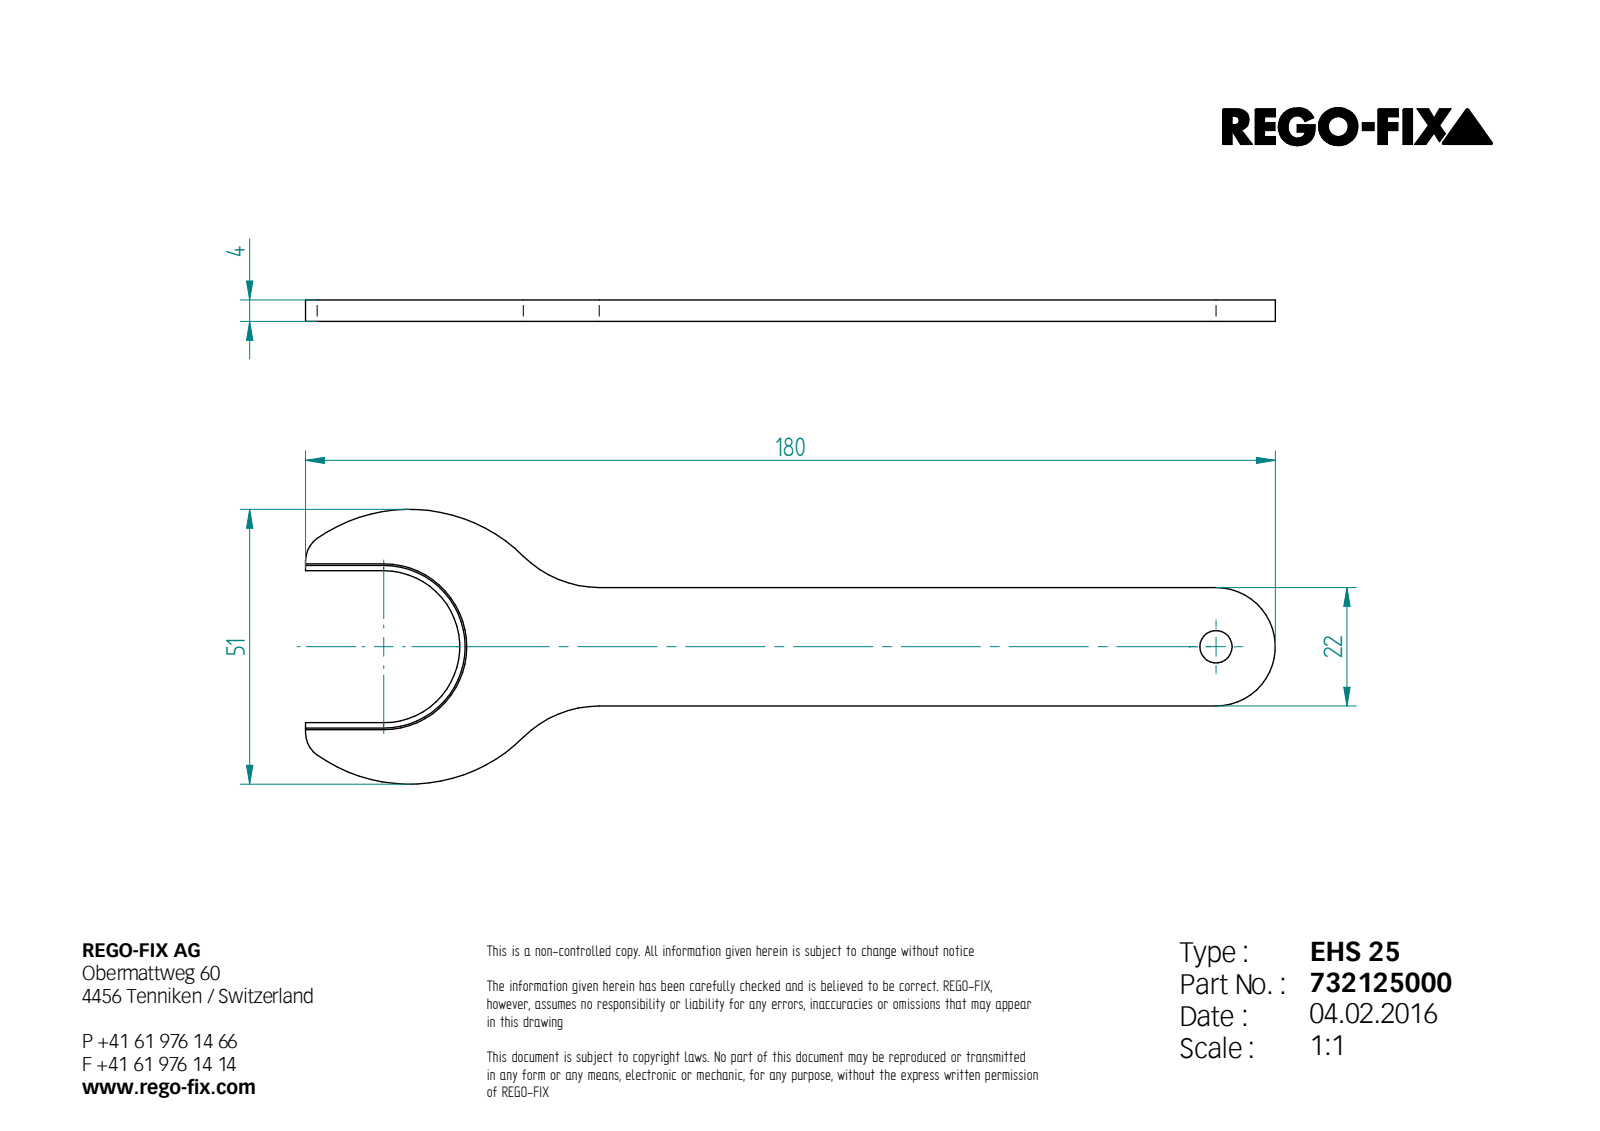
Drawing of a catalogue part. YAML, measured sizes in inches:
step_written_by: "Unknown (AUTOMOTIVE_DESIGN)"
units: inches
bodies: {solids: 1, faces: 23, planar: 12, cylindrical: 9, other: 2}
overall_size: [7.087, 2.008, 0.157]
volume: 1.004
surface_area: 15.87
round_holes:
  - {diameter: 0.236, count: 1}
partial_cylinders:
  - {radius: 0.197, count: 2}
  - {radius: 0.787, count: 2}
  - {radius: 1.181, count: 2}
  - {radius: 0.433, count: 1}
  - {radius: 0.594, count: 1}
face_to_face_distances: [0.157, 0.866, 0.161, 1.028, 1.189, 0.075]
